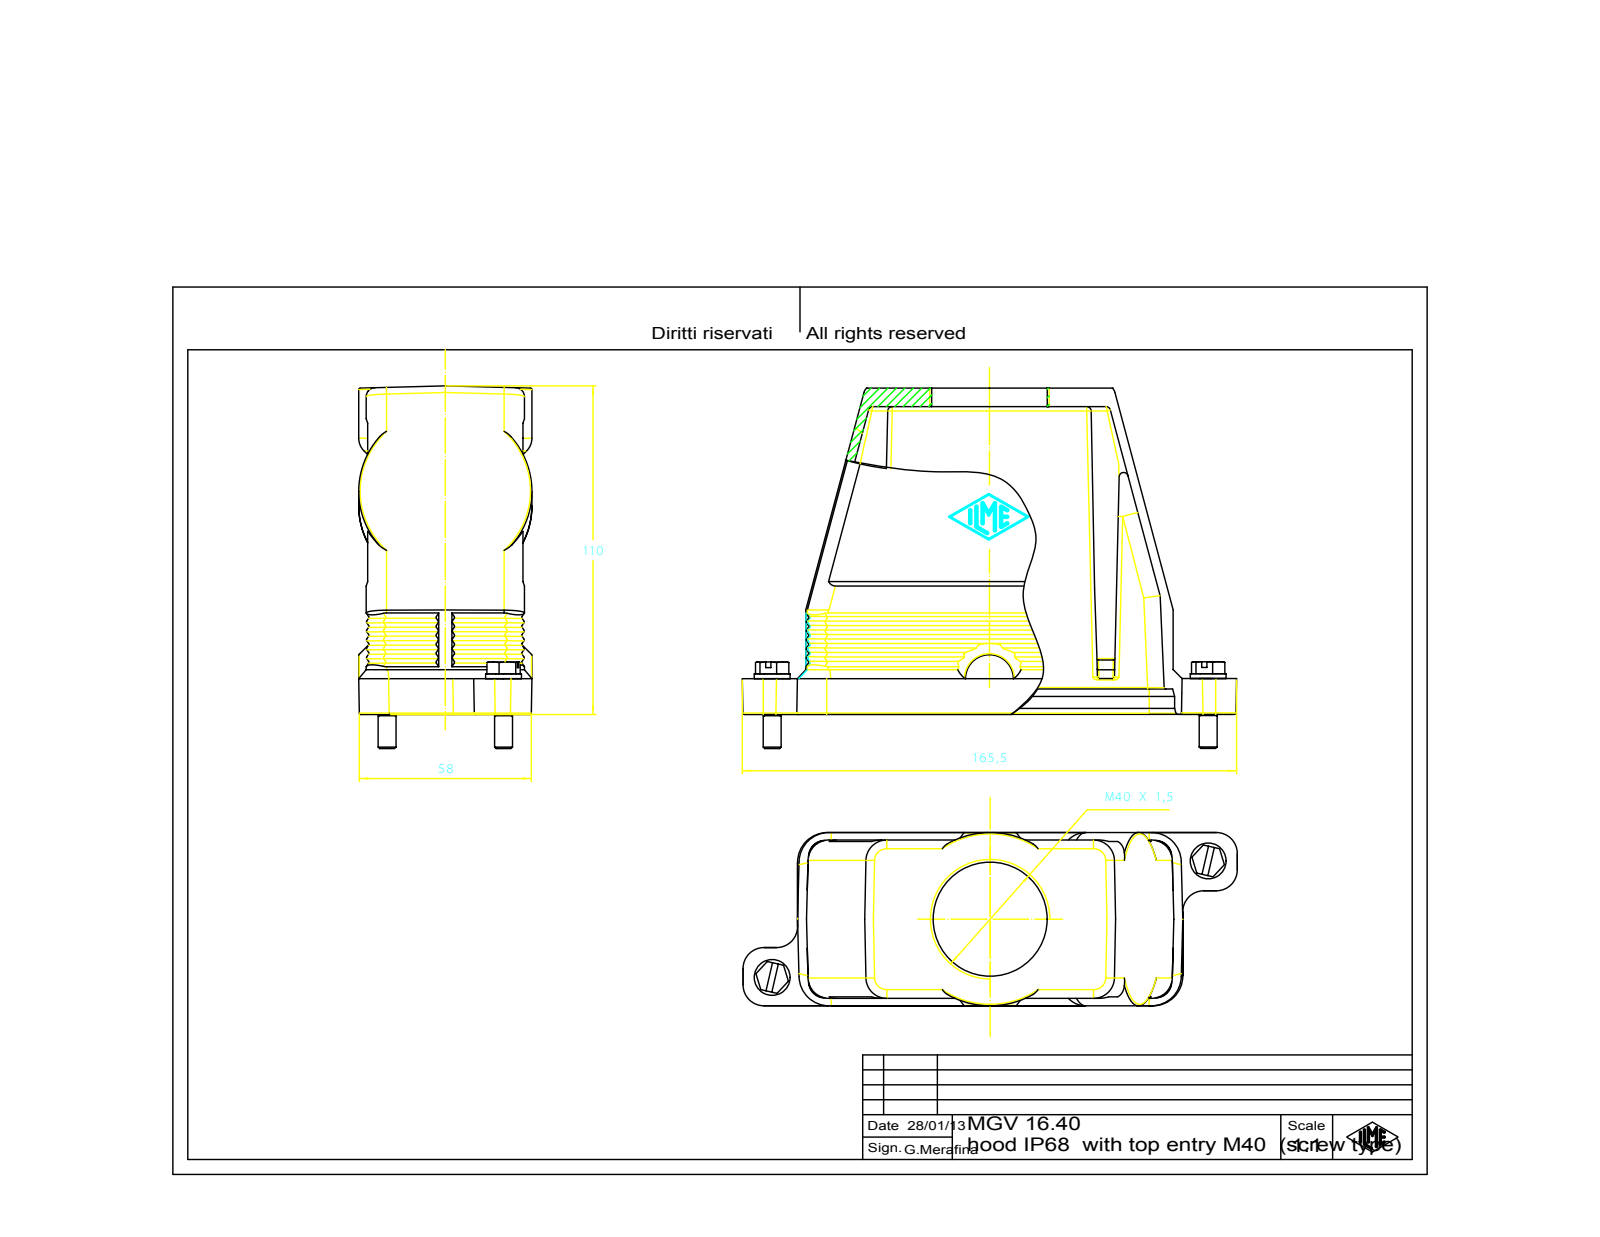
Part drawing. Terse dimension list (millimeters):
name: MGV 16.40
written by: Autodesk Inventor 7 (AUTOMOTIVE_DESIGN)
unit: mm
bodies: 3 solids, 768 faces (190 planar, 195 cylindrical, 383 other)
size: 165 × 122.2 × 58
volume: 221 324 mm³; area: 91 227 mm²
holes: 2× ⌀2.46, 2× ⌀3.2, 2× ⌀6.6, 2× ⌀15, 1× ⌀40
bosses: 2× ⌀58, 2× ⌀56, 2× ⌀12.5, 2× ⌀6
rounds: 39× R0.5, 14× R0.75, 8× R7.5, 6× R6, 4× R1.5, 4× R3, 2× R5.75, 2× R10.5
face distances: 3, 52, 49, 6, 46, 55, 2.5, 0.5, 58, 3.5
hole spacings: 34.69, 116.38, 82.07, 150.86
